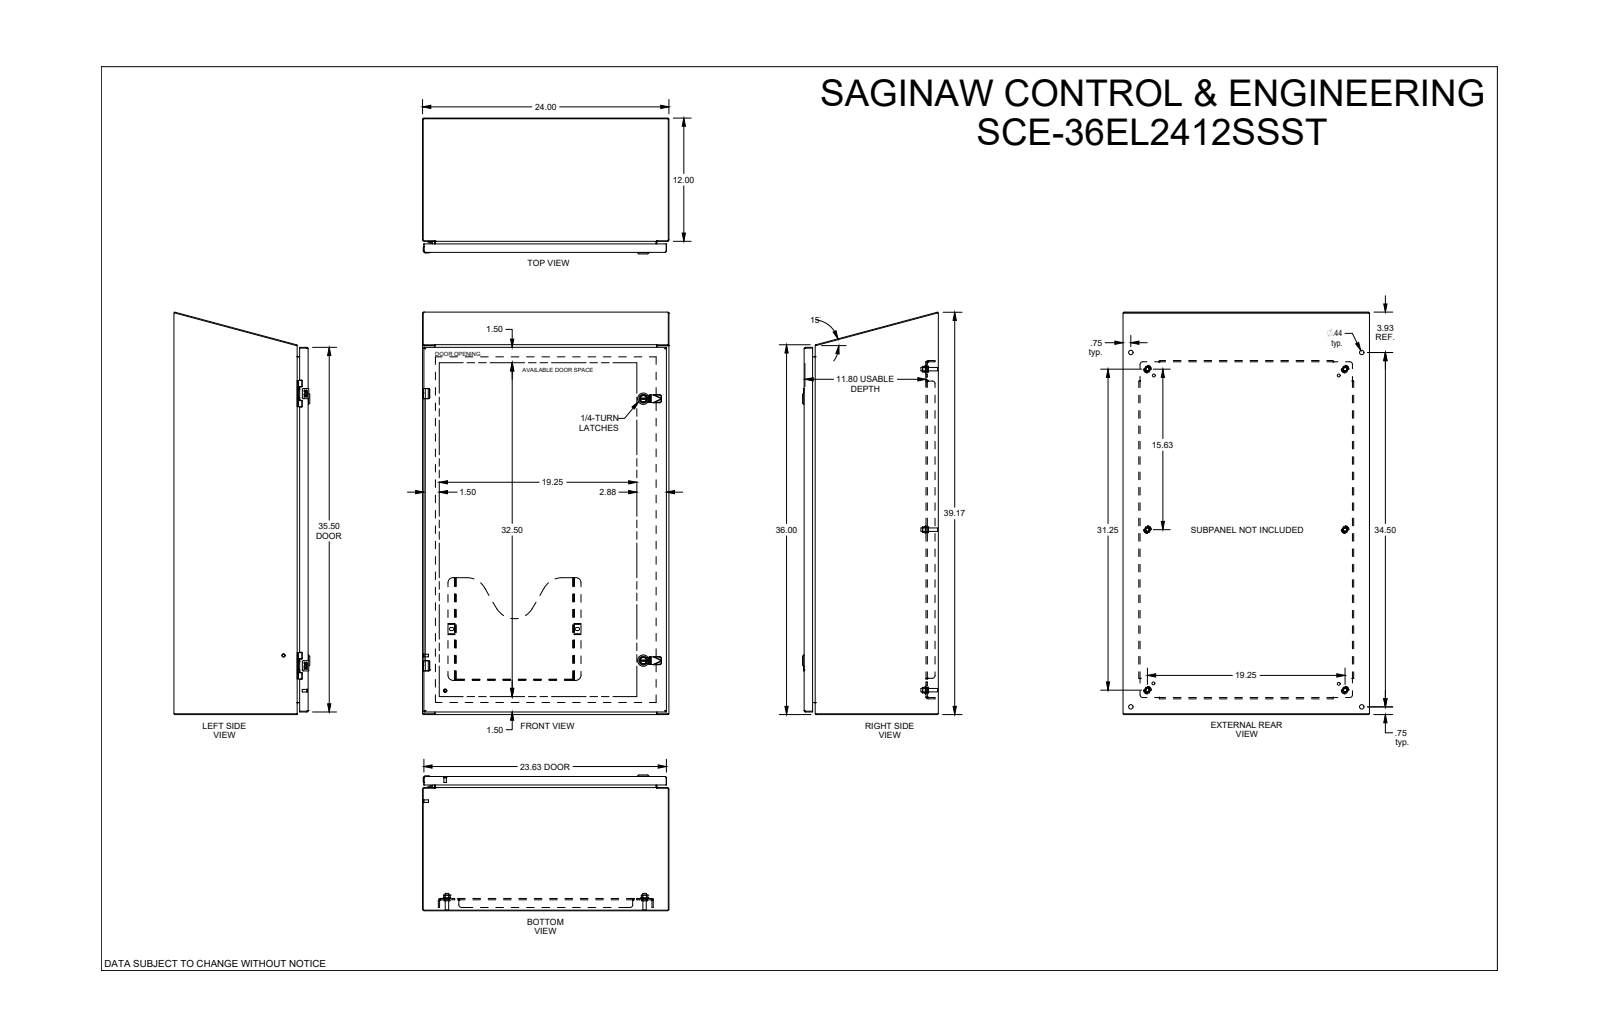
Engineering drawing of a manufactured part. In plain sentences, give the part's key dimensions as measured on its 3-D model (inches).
The part is named "SCE-36EL2412SSST". Its 3-D file was written by "SolidWorks 2019 (CONFIG_CONTROL_DESIGN)". It is 0 solids with 2954 faces: 1335 planar, 779 cylindrical and 840 other. Overall it measures 39.178 by 24 by 13.23 inches. Round holes: 6 of diameter 0.367, 6 of diameter 0.5, 4 of diameter 0.172, 4 of diameter 0.205, 4 of diameter 0.244, 4 of diameter 0.266, 4 of diameter 0.281, 4 of diameter 0.375, 4 of diameter 0.437, 2 of diameter 0.156, 2 of diameter 0.197, 2 of diameter 0.218. Round bosses or shafts: 6 of diameter 0.366, 6 of diameter 0.332, 6 of diameter 0.17, 4 of diameter 0.25, 4 of diameter 0.248, 3 of diameter 0.196, 2 of diameter 1.102, 2 of diameter 0.866. Partial cylindrical surfaces (rounded edges, fillets, slot ends): 56 of radius 0.012, 40 of radius 0.01, 32 of radius 0.015, 23 of radius 0.04, 20 of radius 0.02, 12 of radius 0.029, 11 of radius 0.06, 10 of radius 0.07. The main face-to-face distances are 0.075, 0.075, 12.998, 12.923, 23.925, 13.073, 12.998, 1.2, 11.873, 1. The hole center spacings are 26.5, 0.985, 0.02, 0.875, 2.298, 4.493, 15.625, 17.326.
